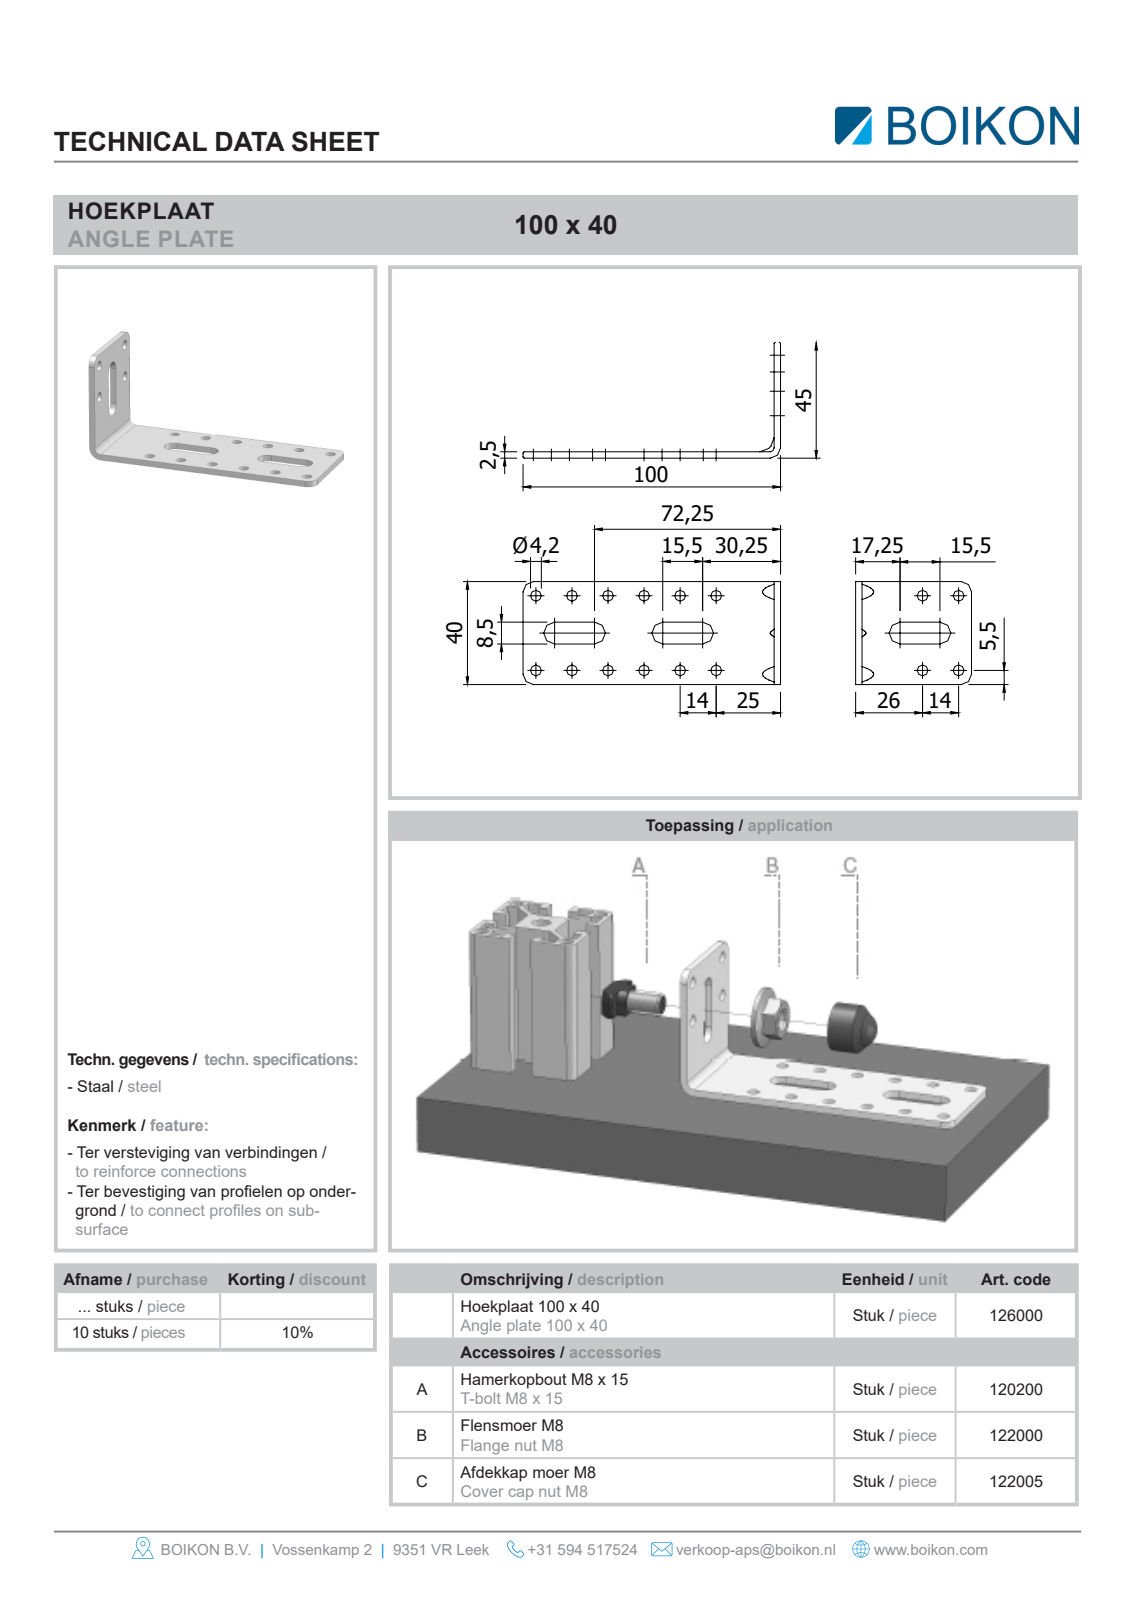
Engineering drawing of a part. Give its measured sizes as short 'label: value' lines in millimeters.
name: Root; 126000Hoekplaat 100 x 40BOIKON; 122000Flensmoer M8BOIKON; 122005Afdekkap voor moer M8BOIKON (+1 more)
written by: HiCAD 2013 1802.4 Build 509 (AUTOMOTIVE_DESIGN)
unit: mm
bodies: 10 solids, 330 faces (221 planar, 70 cylindrical, 39 other)
size: 110.2 × 55.2 × 40
volume: 25 789 mm³; area: 21 338 mm²
holes: 16× ⌀4.2, 3× ⌀8
bosses: 3× ⌀21, 3× ⌀16.8, 3× ⌀6.47
rounds: 12× R1, 6× R0.4, 6× R4.25, 4× R4, 4× R5, 3× R9.7, 1× R2.5
face distances: 2.5, 13, 24.25, 15.75, 9.5, 7, 8.5, 13.5, 26.5, 40
hole spacings: 14, 32.2, 28, 29, 40.31, 42, 14.53, 20.86
